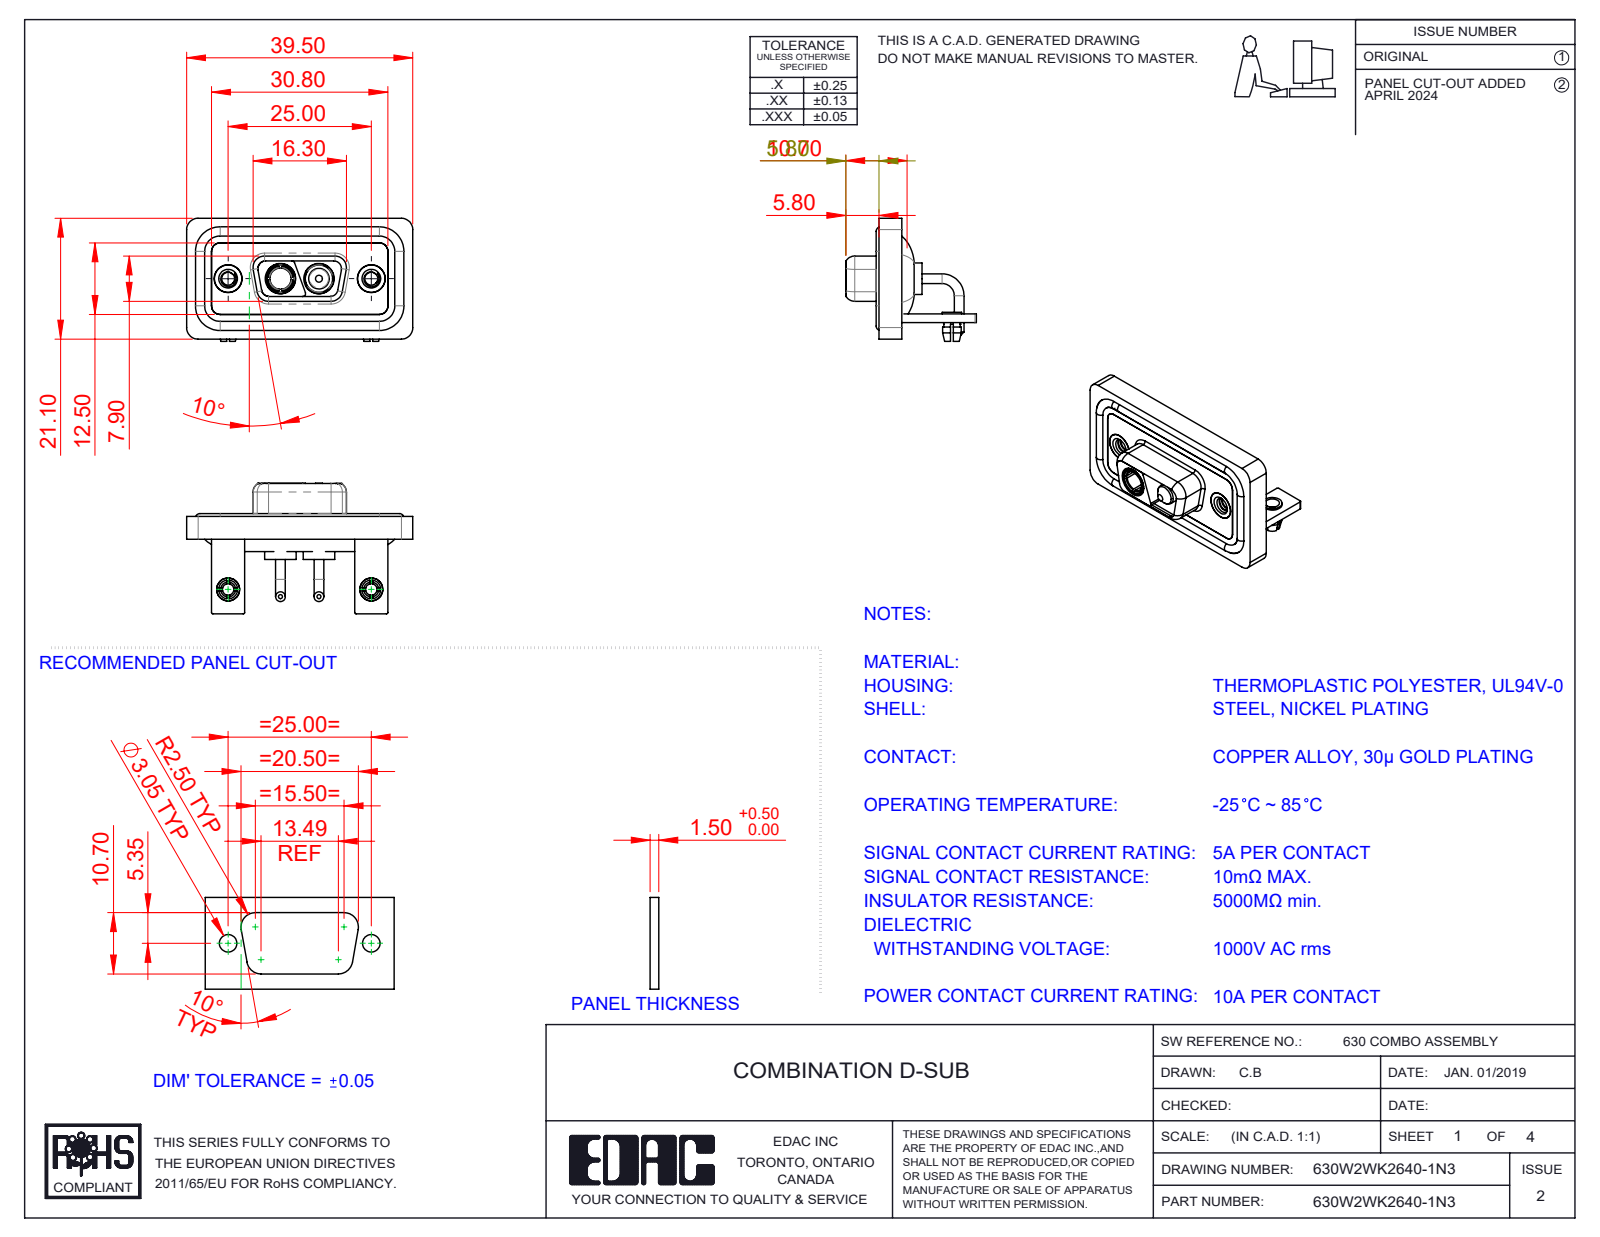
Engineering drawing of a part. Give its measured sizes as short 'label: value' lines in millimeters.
name: Power Socket_10A RA; 630Combo Housing_2WK2; Power Pin_10A RA; 630W2WK2640-1N3 (+6 more)
written by: SolidWorks 2023 (CONFIG_CONTROL_DESIGN)
unit: mm
bodies: 15 solids, 648 faces (212 planar, 291 cylindrical, 145 other)
size: 39.5 × 22.8 × 21.5
volume: 4 994 mm³; area: 8 338 mm²
holes: 4× ⌀4.85, 2× ⌀2, 2× ⌀2.26, 2× ⌀2.5, 2× ⌀3.2, 2× ⌀4, 2× ⌀4.05, 2× ⌀5, 2× ⌀5.3, 1× ⌀3.7
bosses: 4× ⌀1.7, 4× ⌀1.6, 2× ⌀5.5, 2× ⌀5.2, 2× ⌀4.95, 2× ⌀4.8, 2× ⌀4.75, 2× ⌀4
rounds: 19× R2, 18× R1.5, 16× R0.25, 8× R1.35, 8× R1.6, 7× R0.5, 4× R0.6, 4× R0.65
face distances: 0.4, 2.9, 1.5, 1.1, 3.7, 1.8, 0.8, 2.5, 1.6, 3.1
hole spacings: 9.14, 15.86, 25, 6.72
